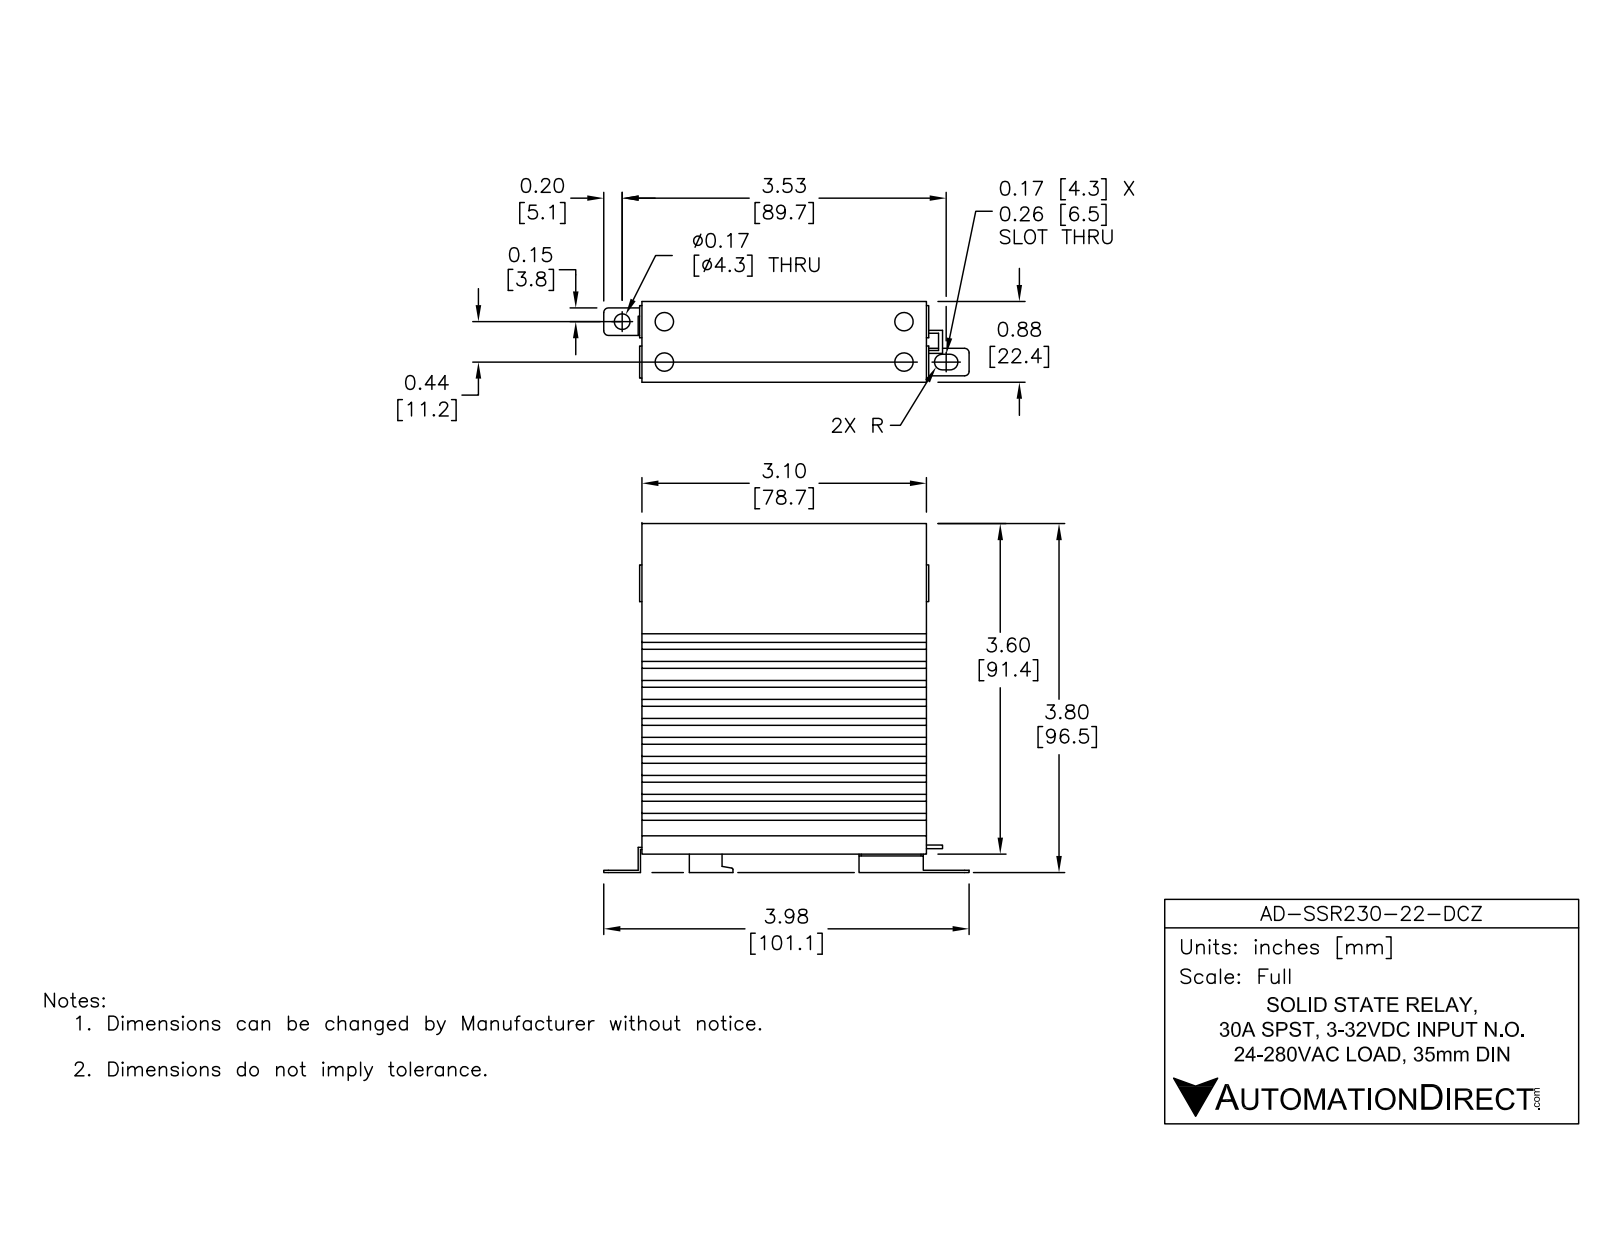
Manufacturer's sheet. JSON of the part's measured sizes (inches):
{"part_name": "AD-SSR230-22-DCZ", "step_written_by": "SolidWorks 2014 (AUTOMOTIVE_DESIGN)", "units": "inches", "bodies": {"solids": 1, "faces": 215, "planar": 195, "cylindrical": 20, "other": 0}, "overall_size": [3.98, 3.8, 0.88], "volume_in3": 7.136, "surface_area_in2": 74.91, "round_holes": [[0.2, 4], [0.17, 1]], "partial_cylinders_radius": [[0.05, 6], [0.085, 2], [0.015, 1]], "face_to_face_distances": [0.62, 0.207, 0.827, 0.414, 0.132, 0.489, 0.339, 0.413, 0.075, 0.207], "hole_center_spacings": [0.44, 2.61, 2.647, 0.46, 0.637, 3.07, 3.102]}
